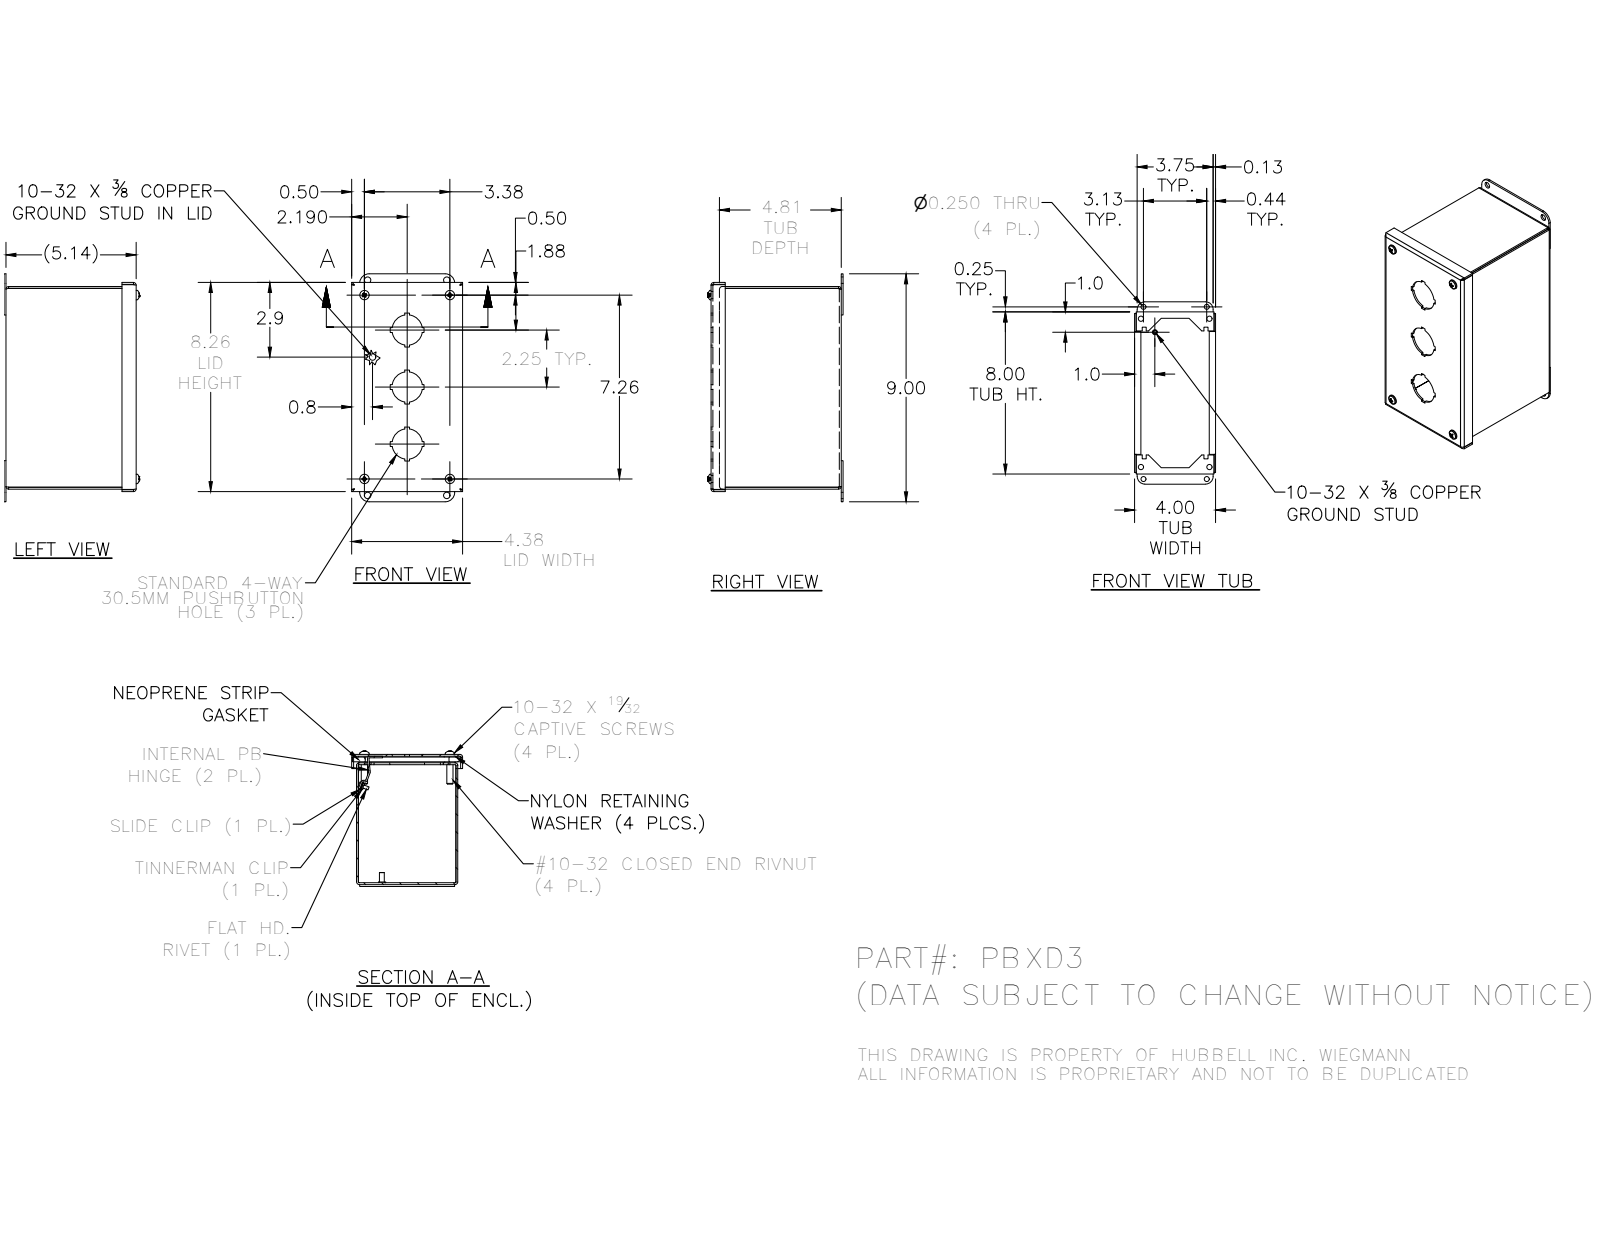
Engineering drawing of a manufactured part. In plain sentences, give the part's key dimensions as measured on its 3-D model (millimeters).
The part is named "PBXD3LID; 372163; 39077; PBXD3BKP (+8 more)". Its 3-D file was written by "Autodesk Inventor 2016 (AUTOMOTIVE_DESIGN)". It is 25 solids with 657 faces: 399 planar, 144 cylindrical and 114 other. Overall it measures 228.6 by 135.79 by 111.25 millimeters. Its volume is 295 120 cubic millimeters and its surface area 305 315 square millimeters. Round holes: 4 of diameter 3.96, 4 of diameter 4.98, 4 of diameter 6.35, 4 of diameter 6.53, 4 of diameter 7.06, 4 of diameter 7.14, 4 of diameter 7.95, 3 of diameter 30.48, 2 of diameter 3.56. Round bosses or shafts: 6 of diameter 4.83, 4 of diameter 11.51, 4 of diameter 10.31, 4 of diameter 9.47, 4 of diameter 6.3, 3 of diameter 6.35, 1 of diameter 3.17. Partial cylindrical surfaces (rounded edges, fillets, slot ends): 12 of radius 0.79, 12 of radius 2.67, 6 of radius 4.78, 4 of radius 2.27, 4 of radius 2.29, 4 of radius 9.53, 3 of radius 0.8, 3 of radius 1.59. The main face-to-face distances are 1.88, 99.72, 128.73, 130.61, 97.84, 101.6, 201.32, 126.85, 203.2, 199.44. The hole center spacings are 101.7, 200.94, 85.85, 1.3, 1.52, 2.1, 15.33, 15.34.
